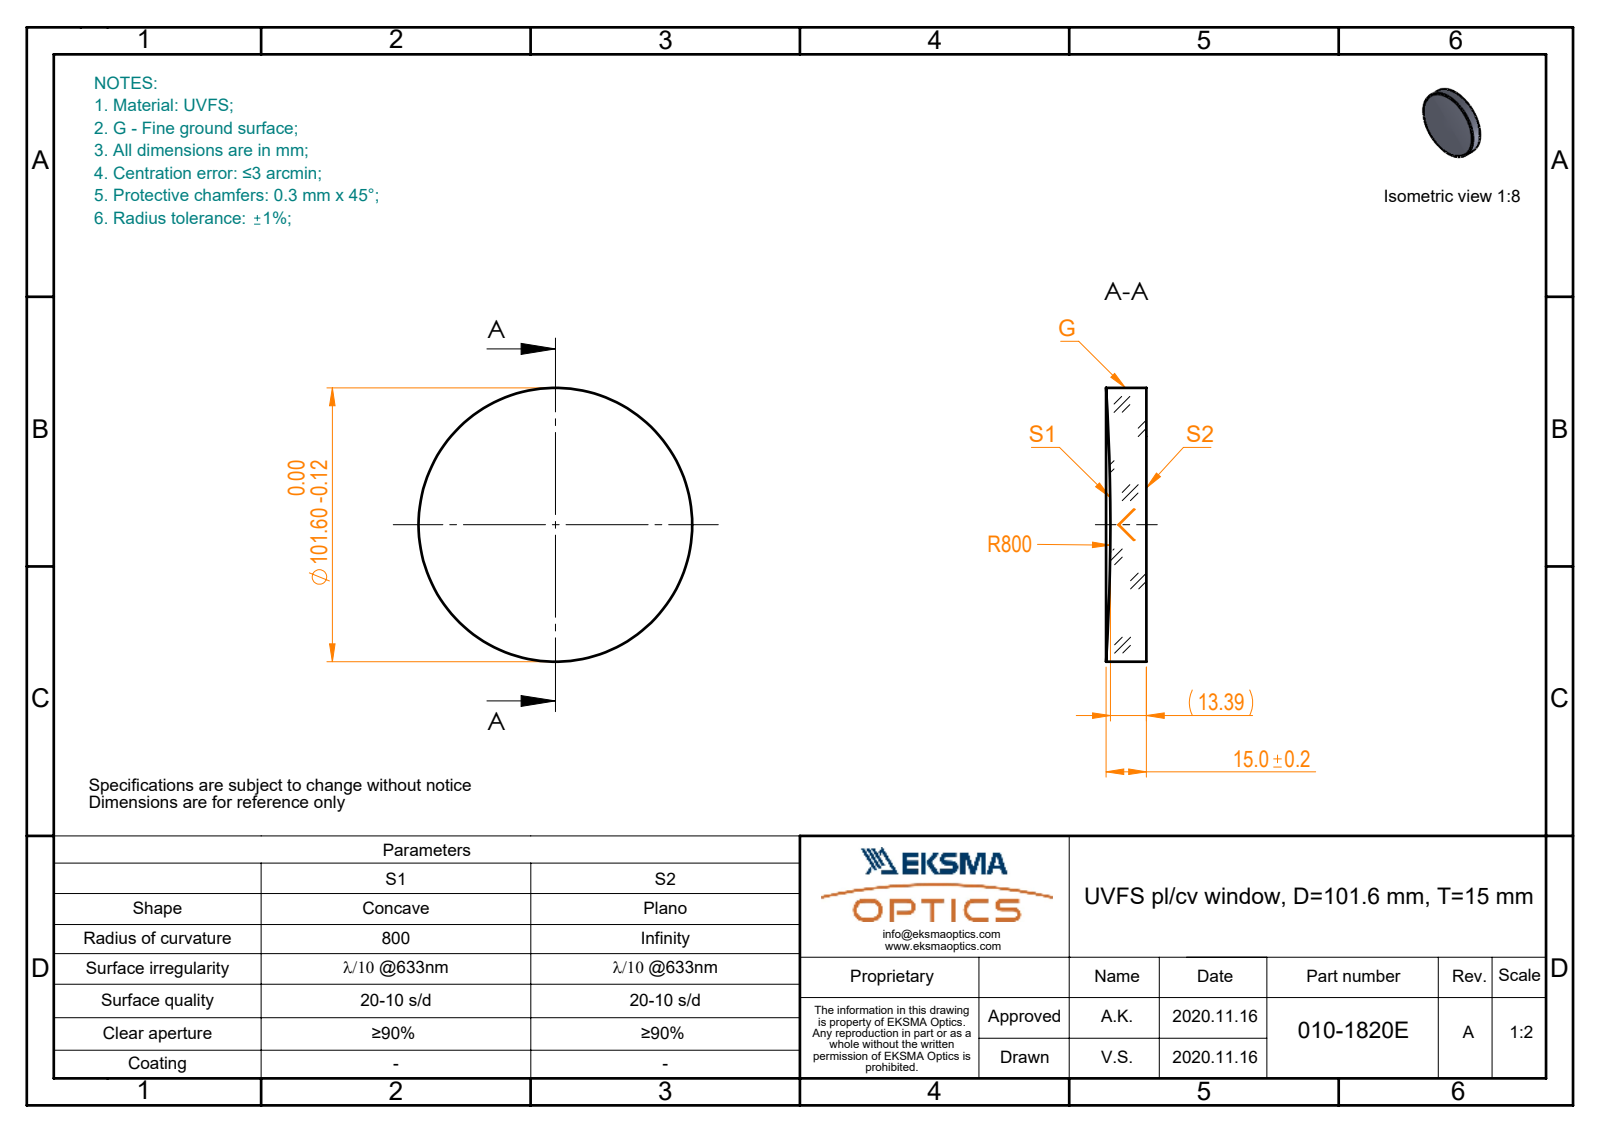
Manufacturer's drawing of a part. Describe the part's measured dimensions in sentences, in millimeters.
The part is named "010-1820E_UVFS_PCV_window". Its 3-D file was written by "SolidWorks 2019 (CONFIG_CONTROL_DESIGN)". It is 1 solid with 5 faces: 1 planar, 2 cylindrical and 2 other. Overall it measures 101.6 by 101.6 by 15 millimeters. Its volume is 115 063 cubic millimeters and its surface area 21 011 square millimeters. Round bosses or shafts: 1 of diameter 101.6.
